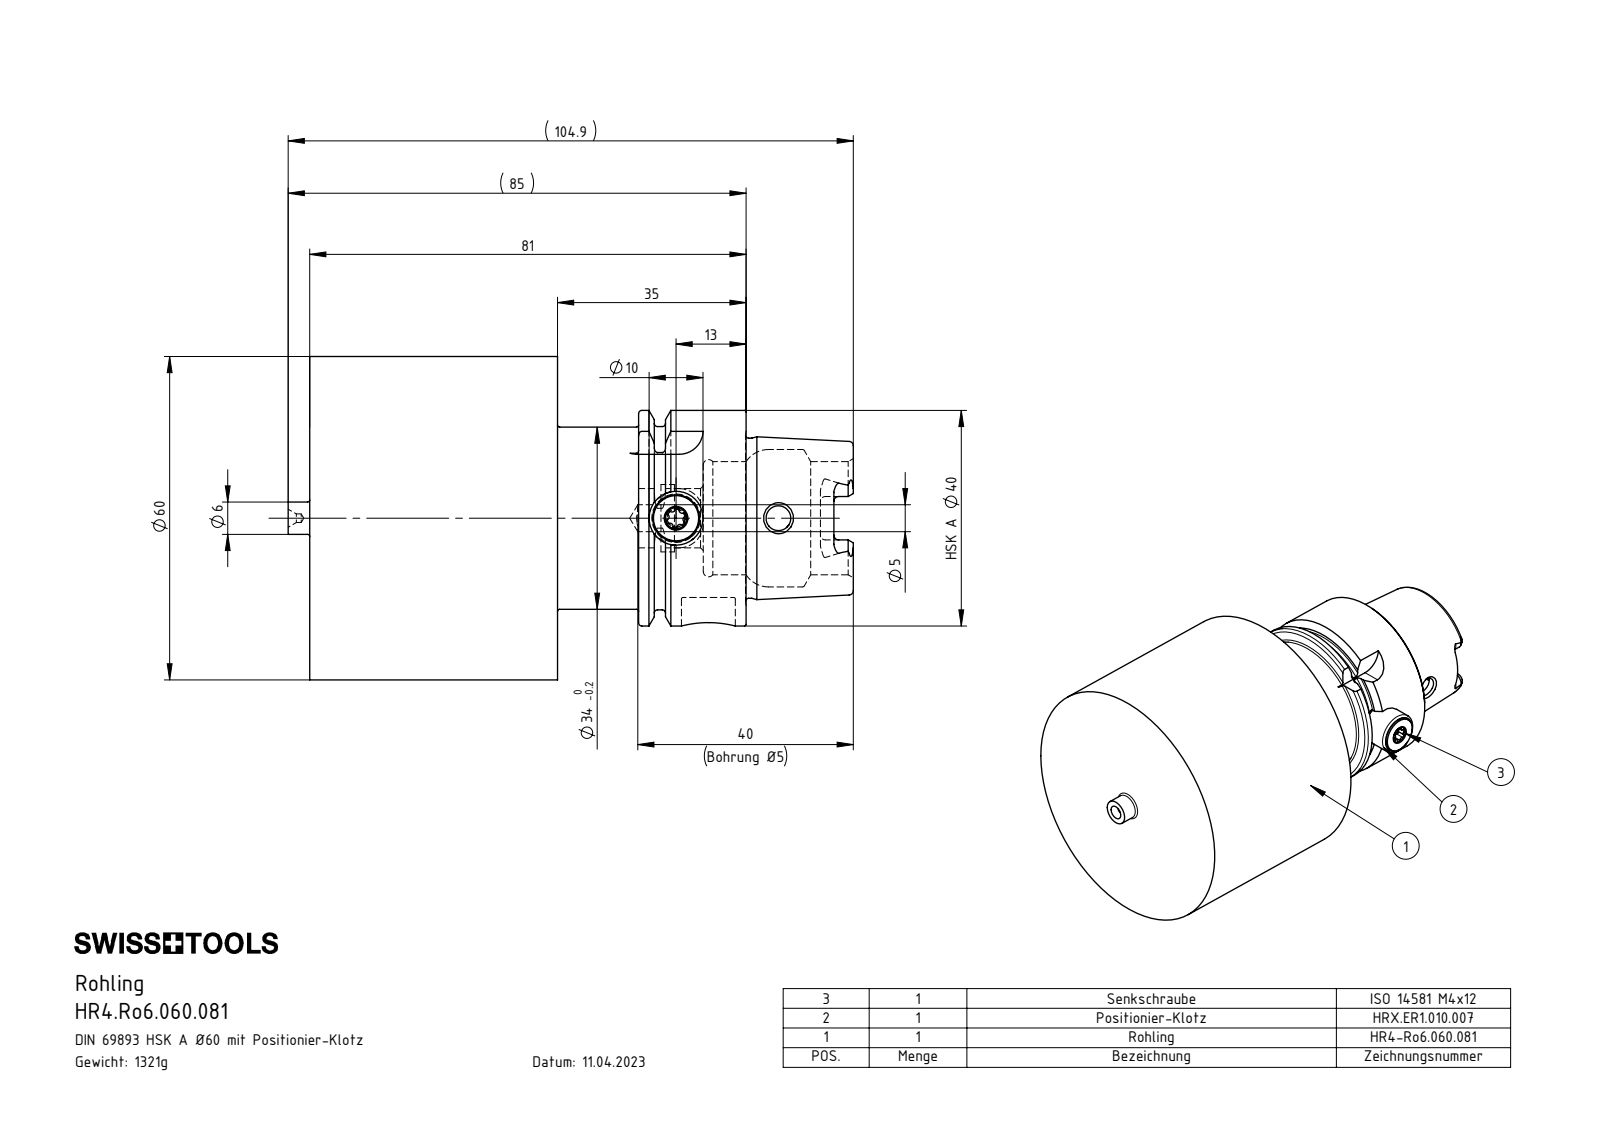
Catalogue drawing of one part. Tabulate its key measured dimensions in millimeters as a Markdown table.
| quantity | value |
| --- | --- |
| part name | HRX-ER1.010.007_A; HR4-Ro6.060.081_A_Fertigbearbeitung; ISO 14581 - M4x12; HR4.Ro6.060.081 |
| STEP written by | SolidWorks 2022 (AUTOMOTIVE_DESIGN) |
| units | millimeters |
| bodies | 3 solids, 217 faces (49 planar, 79 cylindrical, 89 other) |
| overall size | 104.9 × 60 × 60 |
| volume | 168 220 mm³ |
| surface area | 24 695 mm² |
| round holes (diameter × count) | 10 × 2, 1.6 × 1, 3.3 × 1, 4.2 × 1, 4.6 × 1, 5 × 1, 11 × 1, 12.5 × 1, 21 × 1, 25.5 × 1 |
| round bosses / shafts (diameter × count) | 60 × 1, 40 × 1, 34 × 1, 33.8 × 1, 29.71 × 1, 8.4 × 1, 6 × 1, 4 × 1 |
| partial cylindrical surfaces (radius × count) | 0.35 × 6, 0.6 × 6, 0.9 × 6, 1.88 × 4, 4.5 × 3, 3.47 × 1 |
| main face-to-face distances | 46, 35, 81, 19.95, 15.05, 61.05, 12, 7.95, 27.05, 73.05 |
| hole center spacings | 19 |
